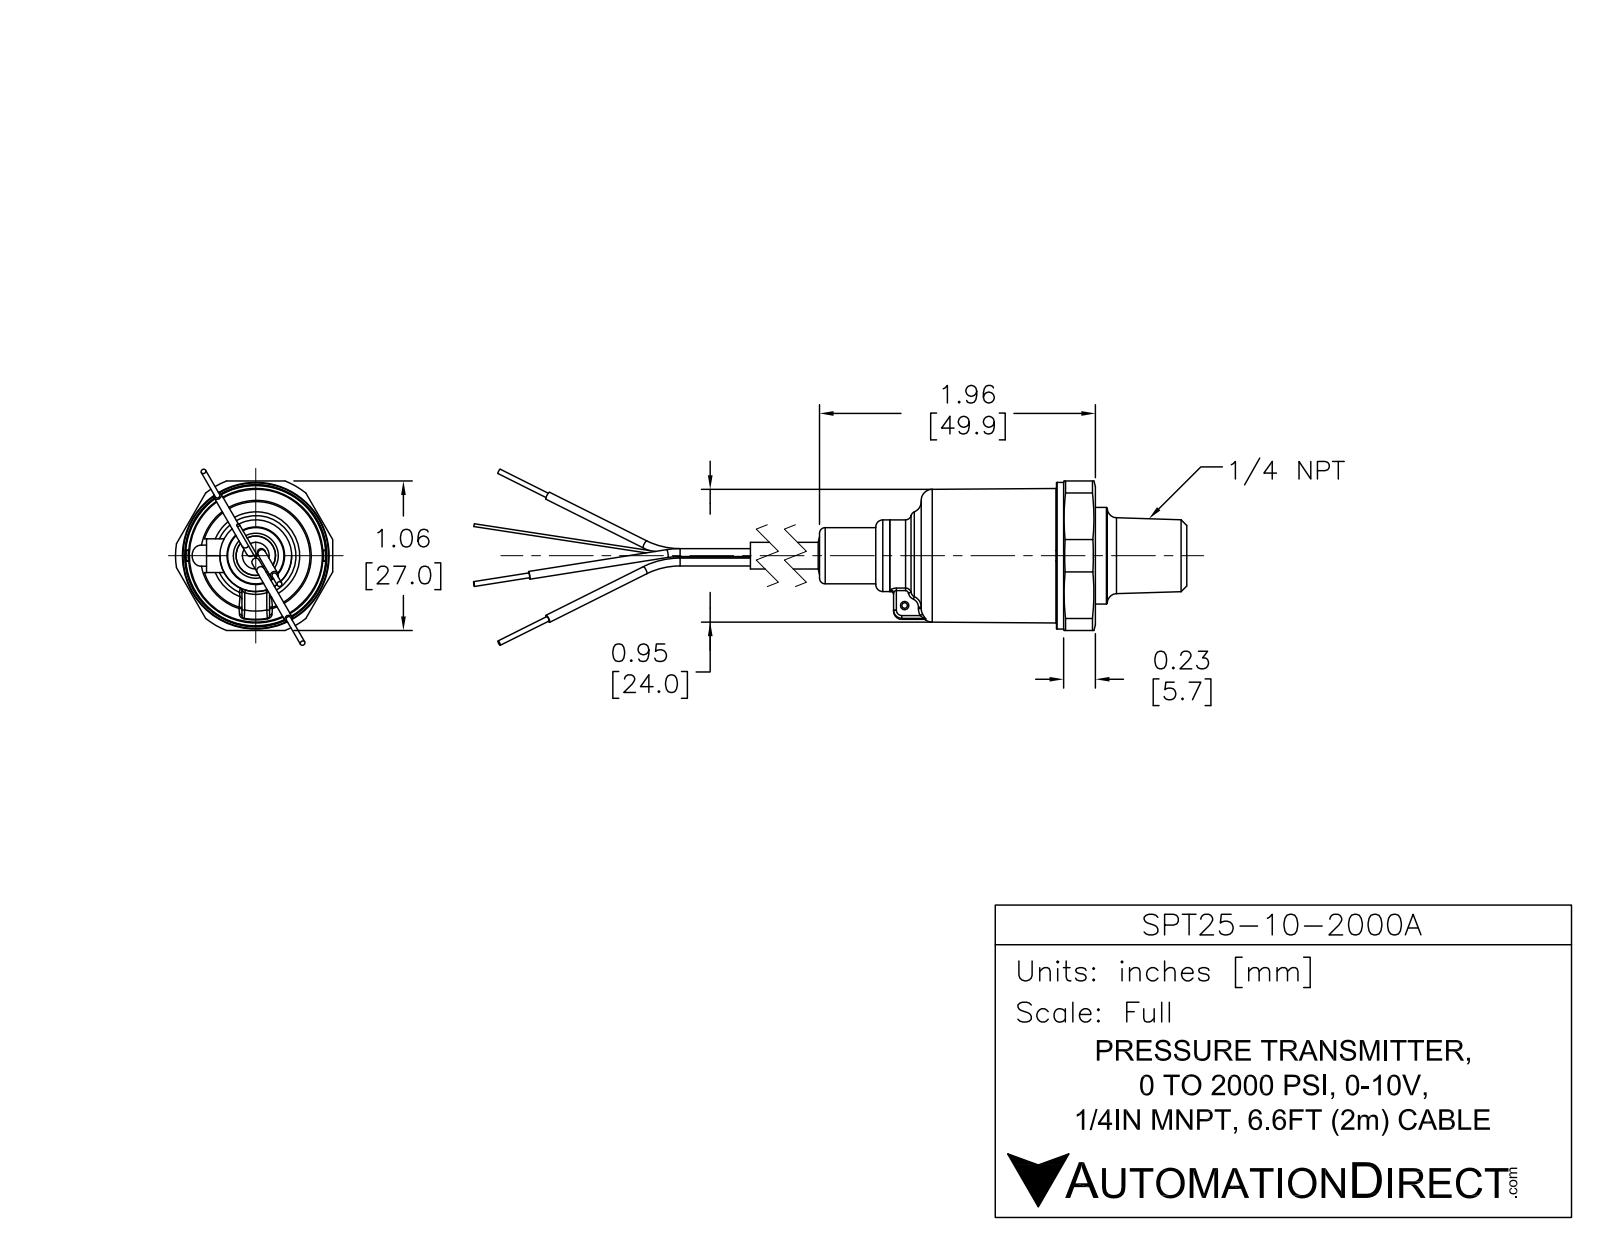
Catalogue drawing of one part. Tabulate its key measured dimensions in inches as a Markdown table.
| quantity | value |
| --- | --- |
| part name | SPT25-10-2000A |
| STEP written by | SolidWorks 2017 (AUTOMOTIVE_DESIGN) |
| units | inches |
| bodies | 7 solids, 116 faces (32 planar, 49 cylindrical, 35 other) |
| overall size | 6.035 × 1.142 × 1.067 |
| volume | 1.269 in³ |
| surface area | 11.11 in² |
| round holes (diameter × count) | 0.039 × 1, 0.13 × 1 |
| round bosses / shafts (diameter × count) | 0.055 × 6, 0.03 × 5, 1.053 × 1, 0.945 × 1, 0.689 × 1, 0.551 × 1, 0.512 × 1, 0.394 × 1 |
| partial cylindrical surfaces (radius × count) | 0.079 × 1, 0.571 × 1 |
| main face-to-face distances | 0.266, 0.945, 0.679, 1.683, 1.949, 2.628, 1.732, 0.049, 0.217, 0.896 |
